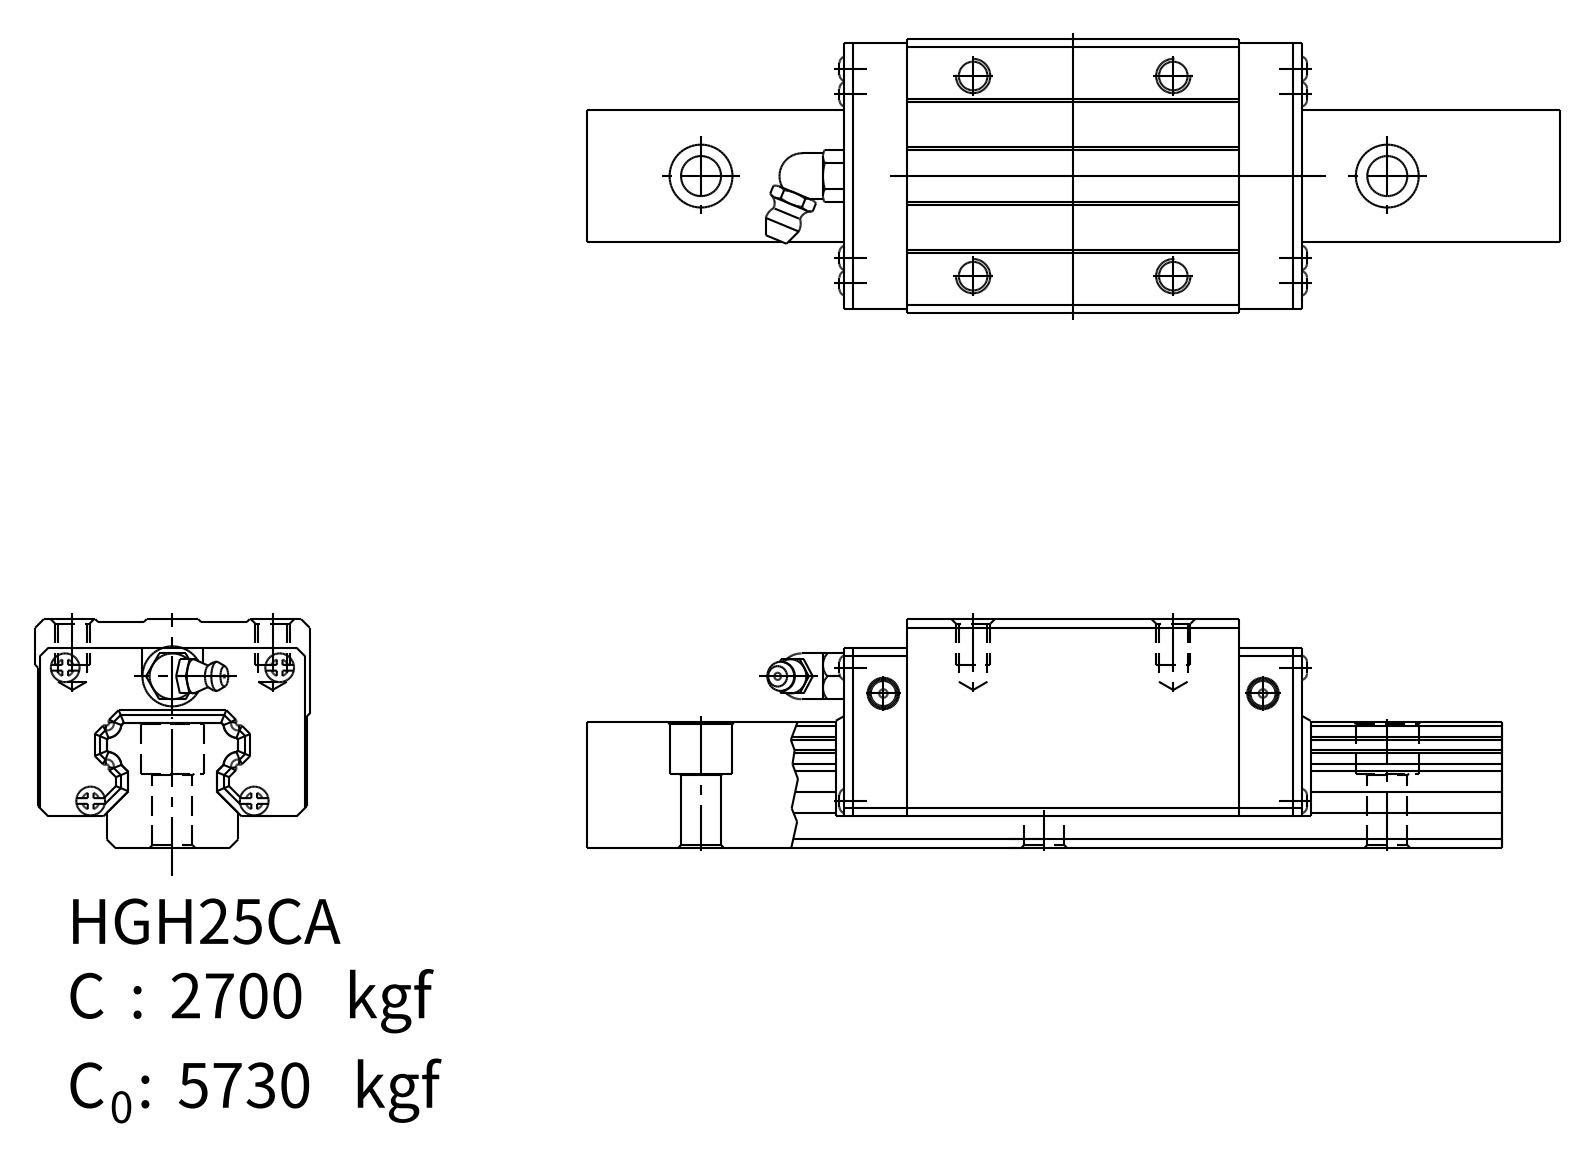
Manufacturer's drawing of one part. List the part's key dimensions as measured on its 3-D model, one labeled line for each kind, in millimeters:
Part name (STEP PRODUCT): HGH25CA
STEP written by: SolidWorks 2006104 (CONFIG_CONTROL_DESIGN)
Units: millimetres
Bodies: 1 solid, 360 faces (270 planar, 30 cylindrical, 60 other)
Overall size (bounding box): 84.3 × 48 × 34.5
Volume: 103 283 mm³ · Surface area: 19 567 mm²
Round holes (diameter × count): ⌀6 ×4
Partial cylindrical surfaces — rounded edges, fillets, slot ends (radius × count): R0.5 ×12, R1 ×6, R2.43 ×4
Main face-to-face distances: 34.5, 47.7, 16.5, 18, 84, 0.5, 34, 17.5, 29.53, 13.03
Hole centre spacings: 35, 49.5
